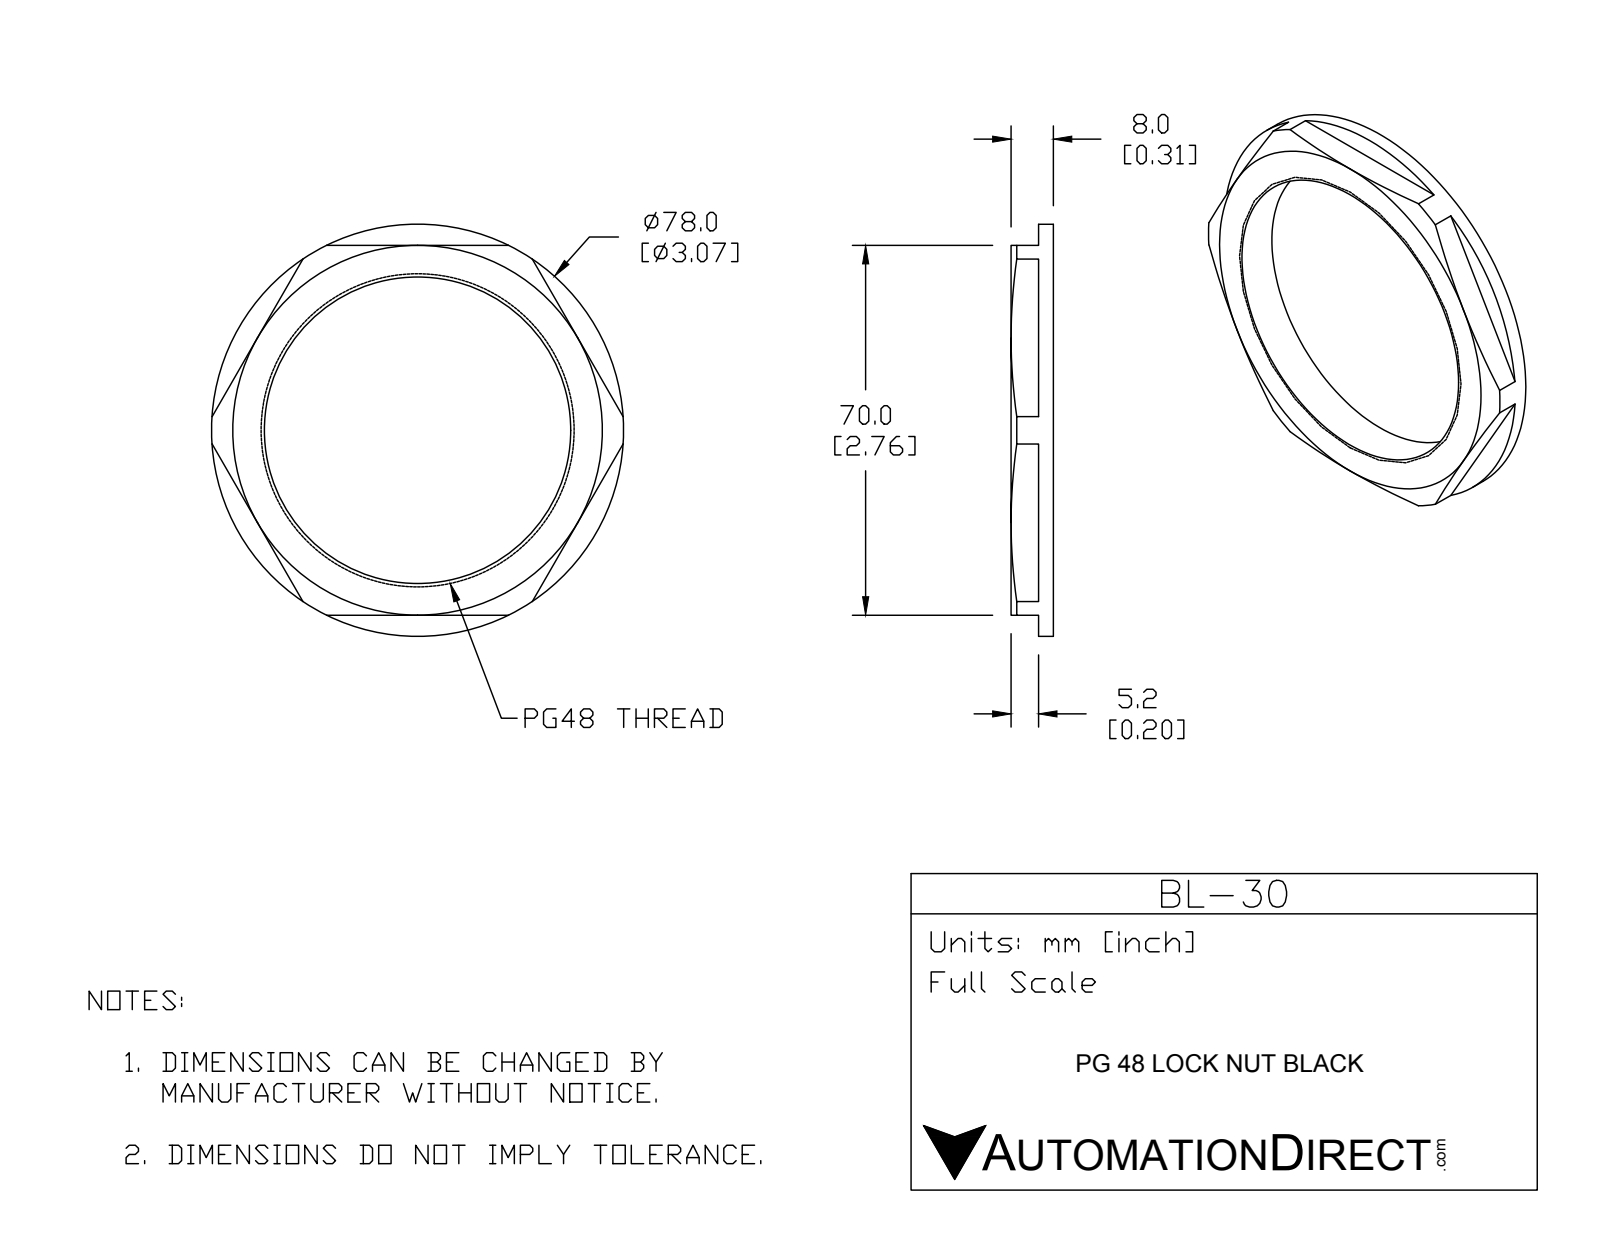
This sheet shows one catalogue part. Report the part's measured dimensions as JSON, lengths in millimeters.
{"part_name": "BL-30", "step_written_by": "SolidWorks 2015 (CONFIG_CONTROL_DESIGN)", "units": "millimeters", "bodies": {"solids": 1, "faces": 33, "planar": 17, "cylindrical": 10, "other": 6}, "overall_size": [78, 78, 8], "volume_mm3": 14048, "surface_area_mm2": 7561, "round_holes": [[1.5, 3], [58, 1]], "round_bosses_or_shafts": [[78, 1]], "face_to_face_distances": [8, 2.8, 5.2, 70, 2.5, 7.7], "hole_center_spacings": [37.55, 65.04, 65.03]}
